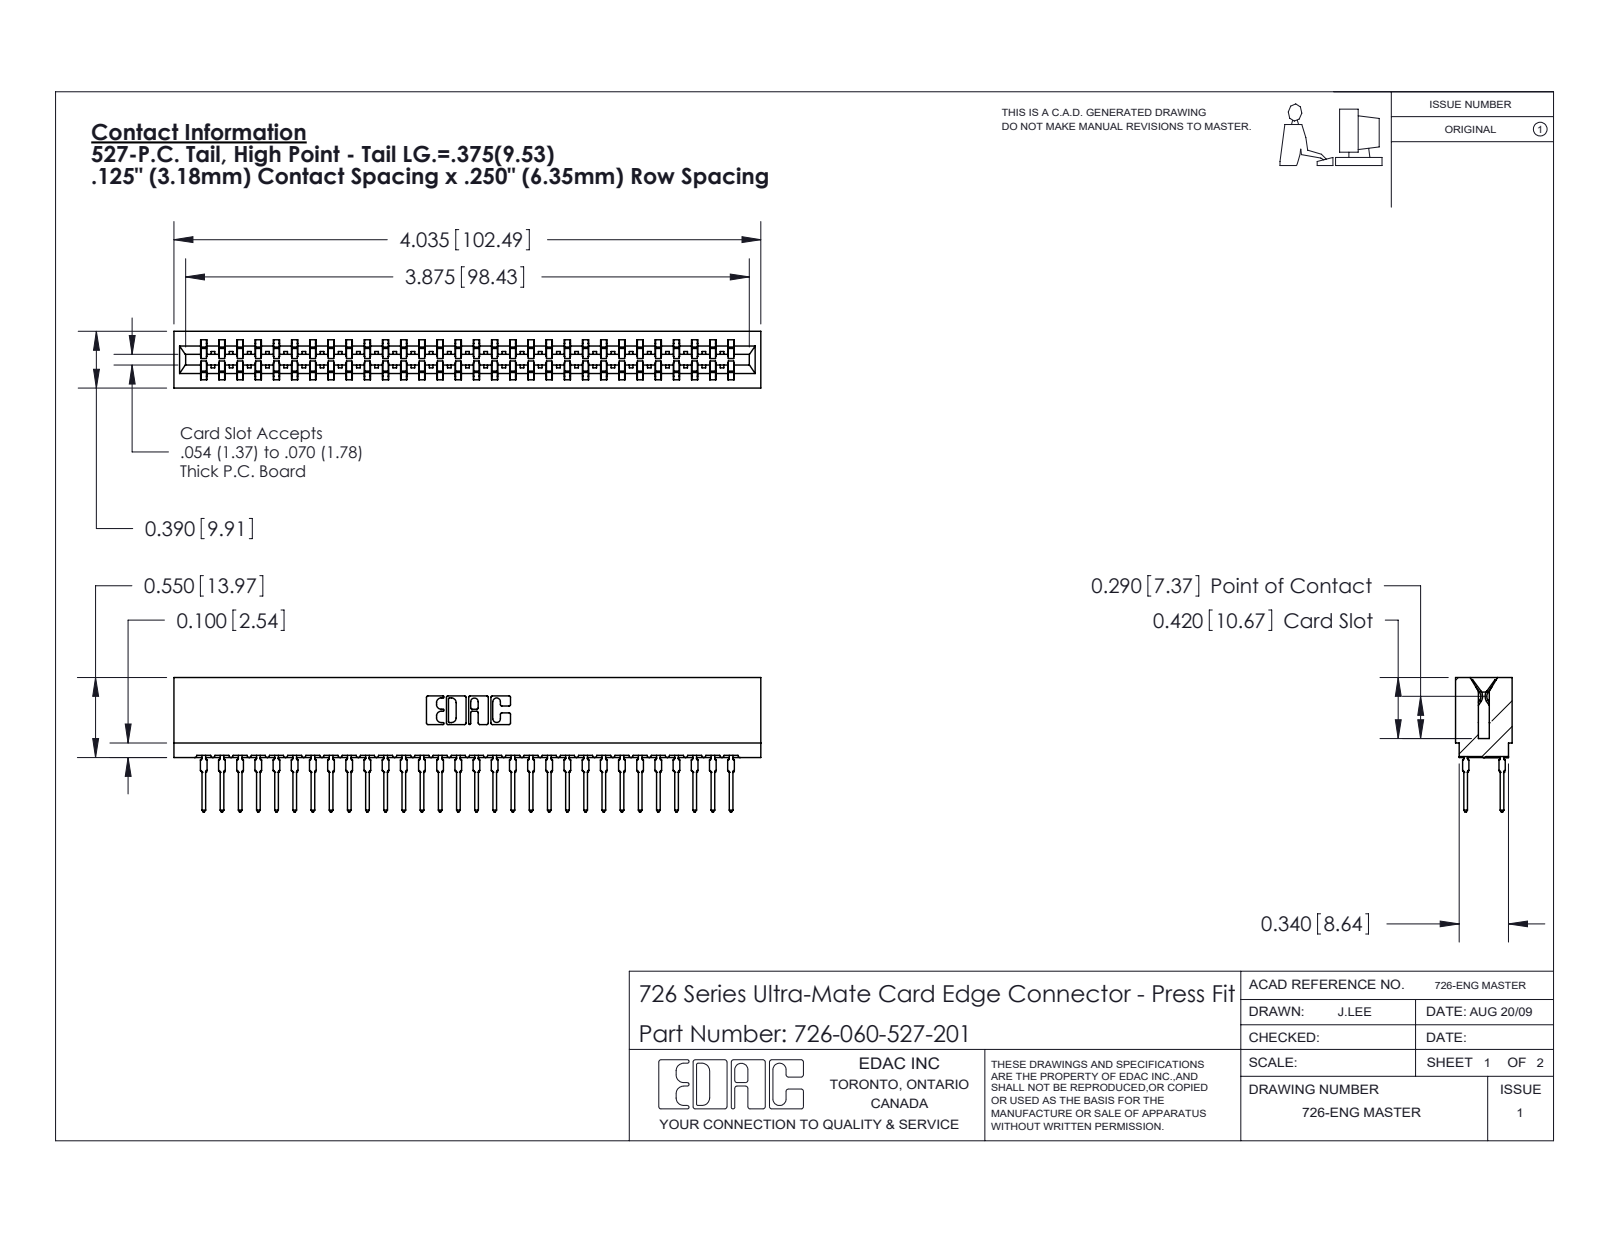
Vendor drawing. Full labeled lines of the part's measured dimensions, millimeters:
Part name (STEP PRODUCT): 746-292-001_527; 726 Part_.515 Slot Depth - 01; 726-060-527-201
STEP written by: SolidWorks 2020 (CONFIG_CONTROL_DESIGN)
Units: millimetres
Bodies: 61 solids, 5467 faces (2815 planar, 1092 cylindrical, 1560 other)
Overall size (bounding box): 102.5 × 23.5 × 9.9
Volume: 9 590 mm³ · Surface area: 16 250 mm²
Partial cylindrical surfaces — rounded edges, fillets, slot ends (radius × count): R0.5 ×120, R0.4 ×31, R0.3 ×22, R0.1 ×8, R0.3 ×8, R0.2 ×6, R0.8 ×6, R0.7 ×3
Main face-to-face distances: 1.4, 8.5, 6.4, 0.6, 7.8, 9.9, 2.1, 7, 12.7, 19.1
